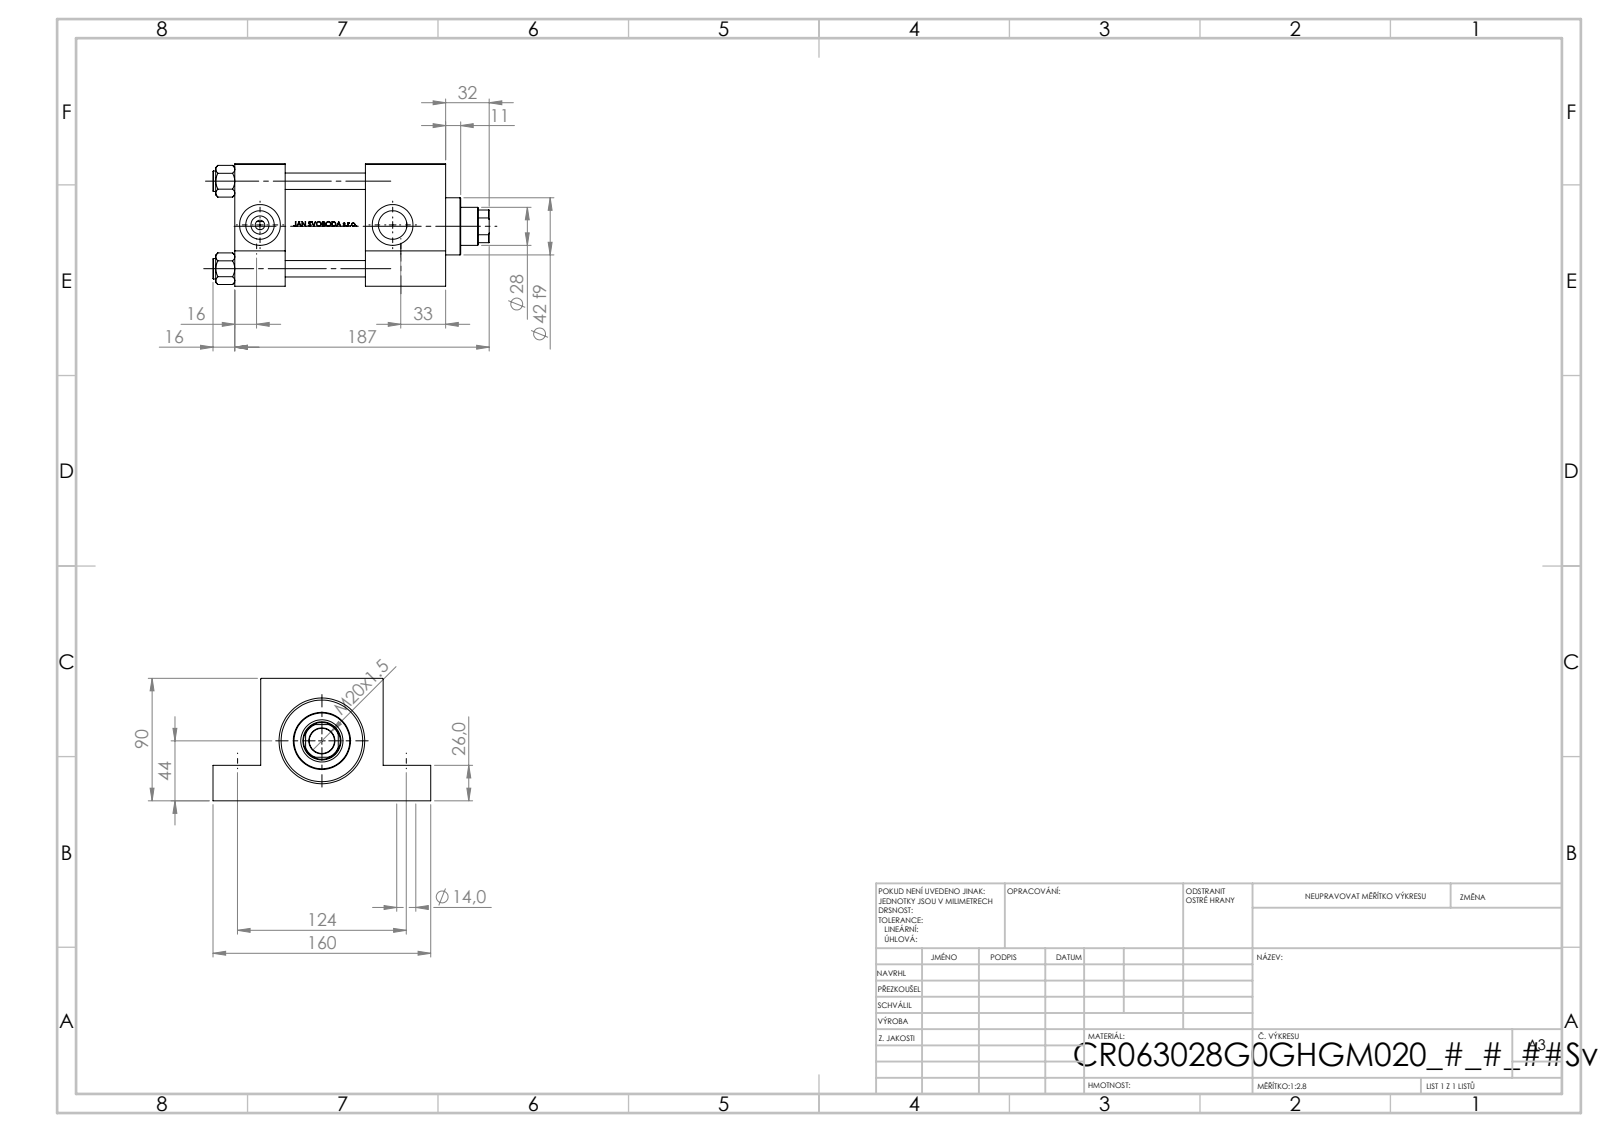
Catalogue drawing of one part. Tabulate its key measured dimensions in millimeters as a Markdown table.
| quantity | value |
| --- | --- |
| part name | V215CR_VCP_G; NUT_M5_G; V215CR_G_TYCINKA; V215_VC_A (+1 more) |
| STEP written by | SolidWorks 2019 (CONFIG_CONTROL_DESIGN) |
| units | millimeters |
| bodies | 11 solids, 1087 faces (431 planar, 124 cylindrical, 532 other) |
| overall size | 203 × 160 × 90 |
| volume | 1 117 000 mm³ |
| surface area | 199 422 mm² |
| round holes (diameter × count) | 12 × 4, 14 × 4, 7 × 2, 20.96 × 2, 30 × 2, 18.5 × 1, 28 × 1, 31 × 1, 50 × 1, 60 × 1, 63 × 1 |
| round bosses / shafts (diameter × count) | 15 × 4, 69 × 1, 42 × 1 |
| partial cylindrical surfaces (radius × count) | 13.5 × 1 |
| main face-to-face distances | 90, 59, 37, 155, 118, 96, 26, 64, 125, 35 |
| hole center spacings | 64.3, 44.77, 46.18, 90.93, 106, 124, 163.13, 97.5 |
